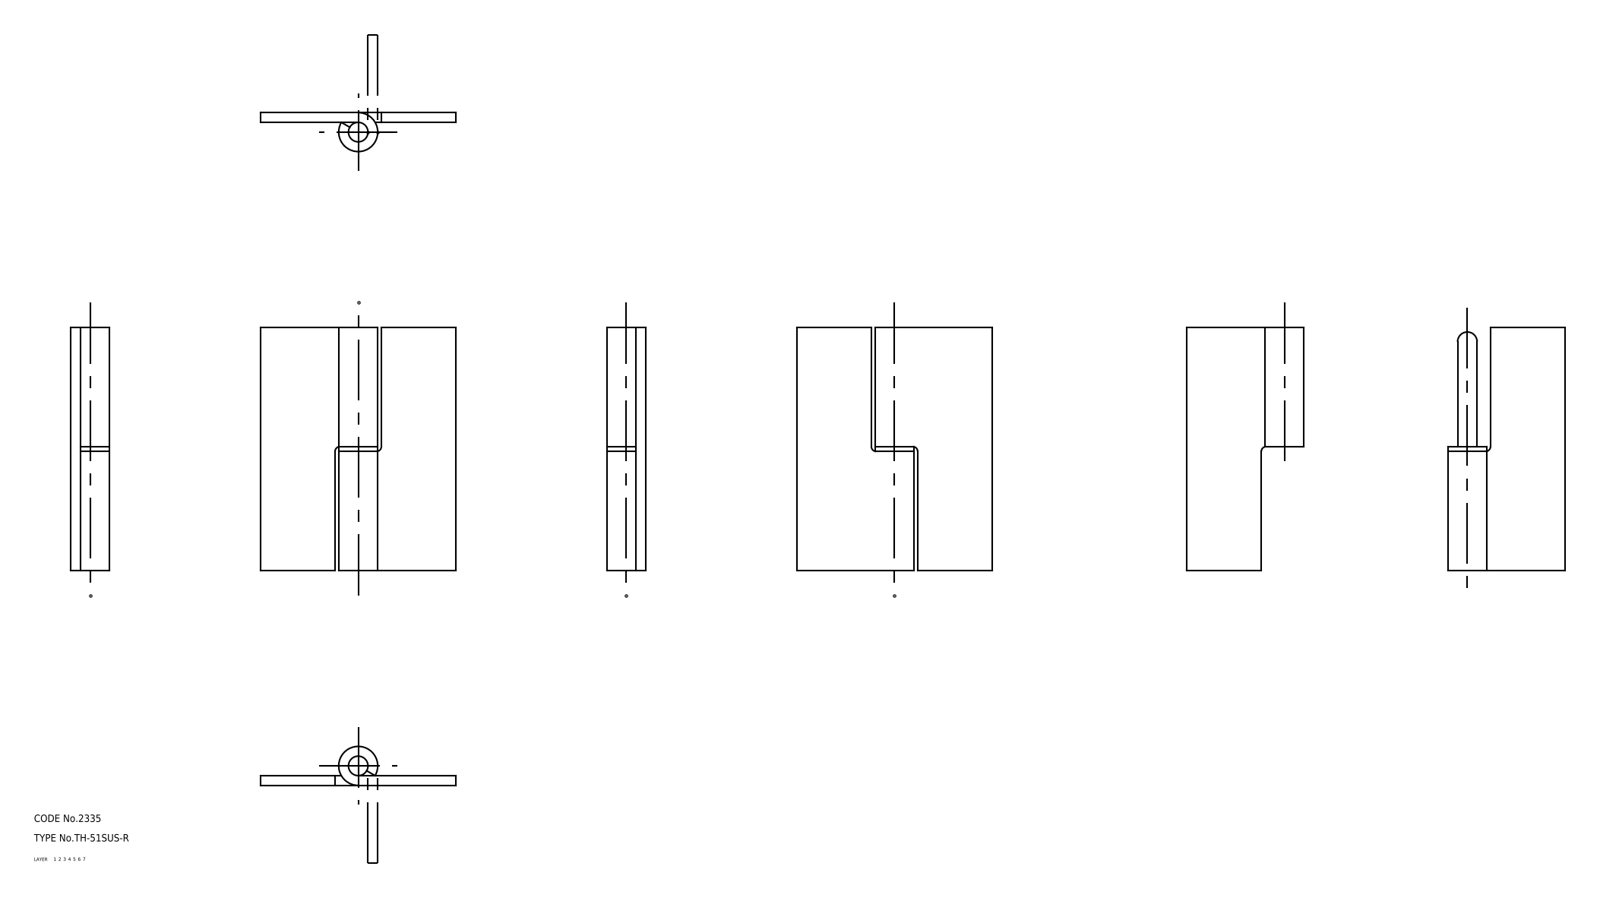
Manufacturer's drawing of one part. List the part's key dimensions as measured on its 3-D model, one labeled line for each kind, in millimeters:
Part name (STEP PRODUCT): washer; shaft; hinge piece_B; hinge piece_A (+1 more)
STEP written by: CADfix (AUTOMOTIVE_DESIGN)
Units: millimetres
Bodies: 4 solids, 30 faces (0 planar, 0 cylindrical, 30 other)
Overall size (bounding box): 100 × 80 × 16
Volume: 45 589 mm³ · Surface area: 25 919 mm²
